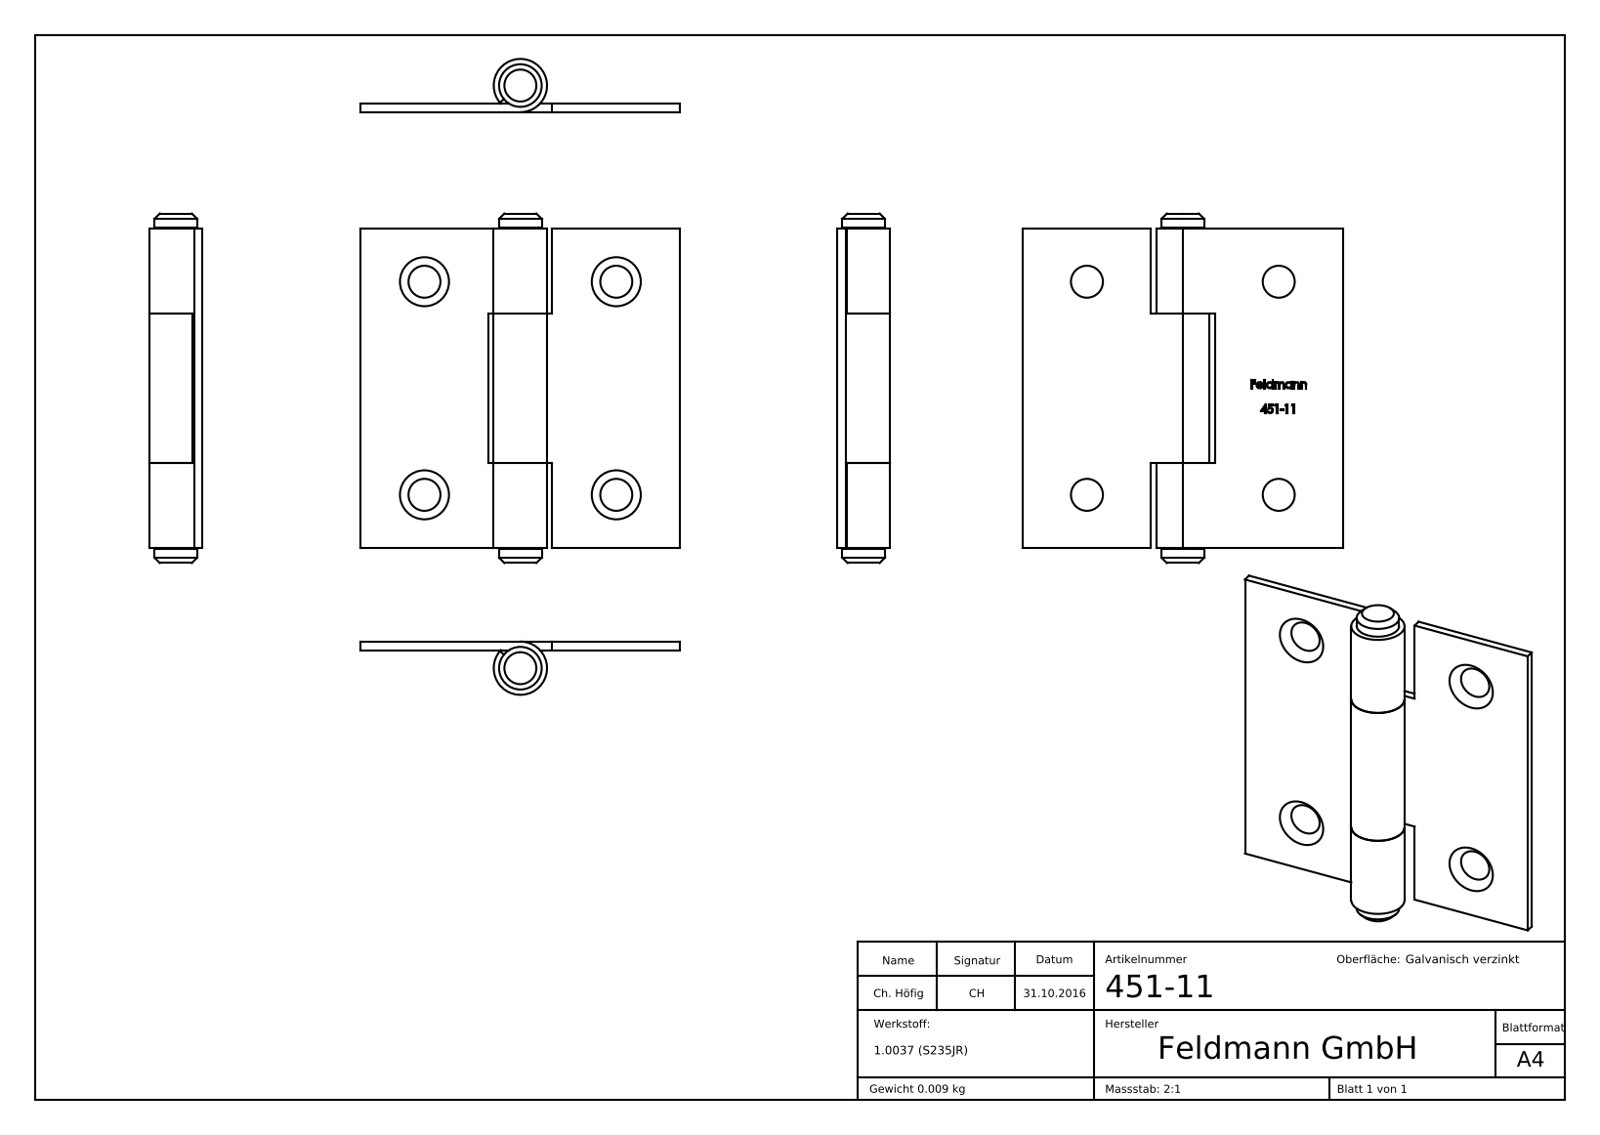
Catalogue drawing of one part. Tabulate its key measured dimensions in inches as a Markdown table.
| quantity | value |
| --- | --- |
| part name | 451-11 Teil2; 451-11 Teil1; 451-11 Teil3; 451-11 |
| STEP written by | SolidWorks 2018 (CONFIG_CONTROL_DESIGN) |
| units | inches |
| bodies | 3 solids, 208 faces (137 planar, 9 cylindrical, 62 other) |
| overall size | 1.291 × 1.181 × 0.197 |
| volume | 0.072 in³ |
| surface area | 4.414 in² |
| round holes (diameter × count) | 0.134 × 1 |
| round bosses / shafts (diameter × count) | 0.197 × 1, 0.157 × 1 |
| main face-to-face distances | 0.031, 1.181, 0.315, 0.866, 0.472, 0.709, 0.551, 0.055, 0.37, 0.921 |
